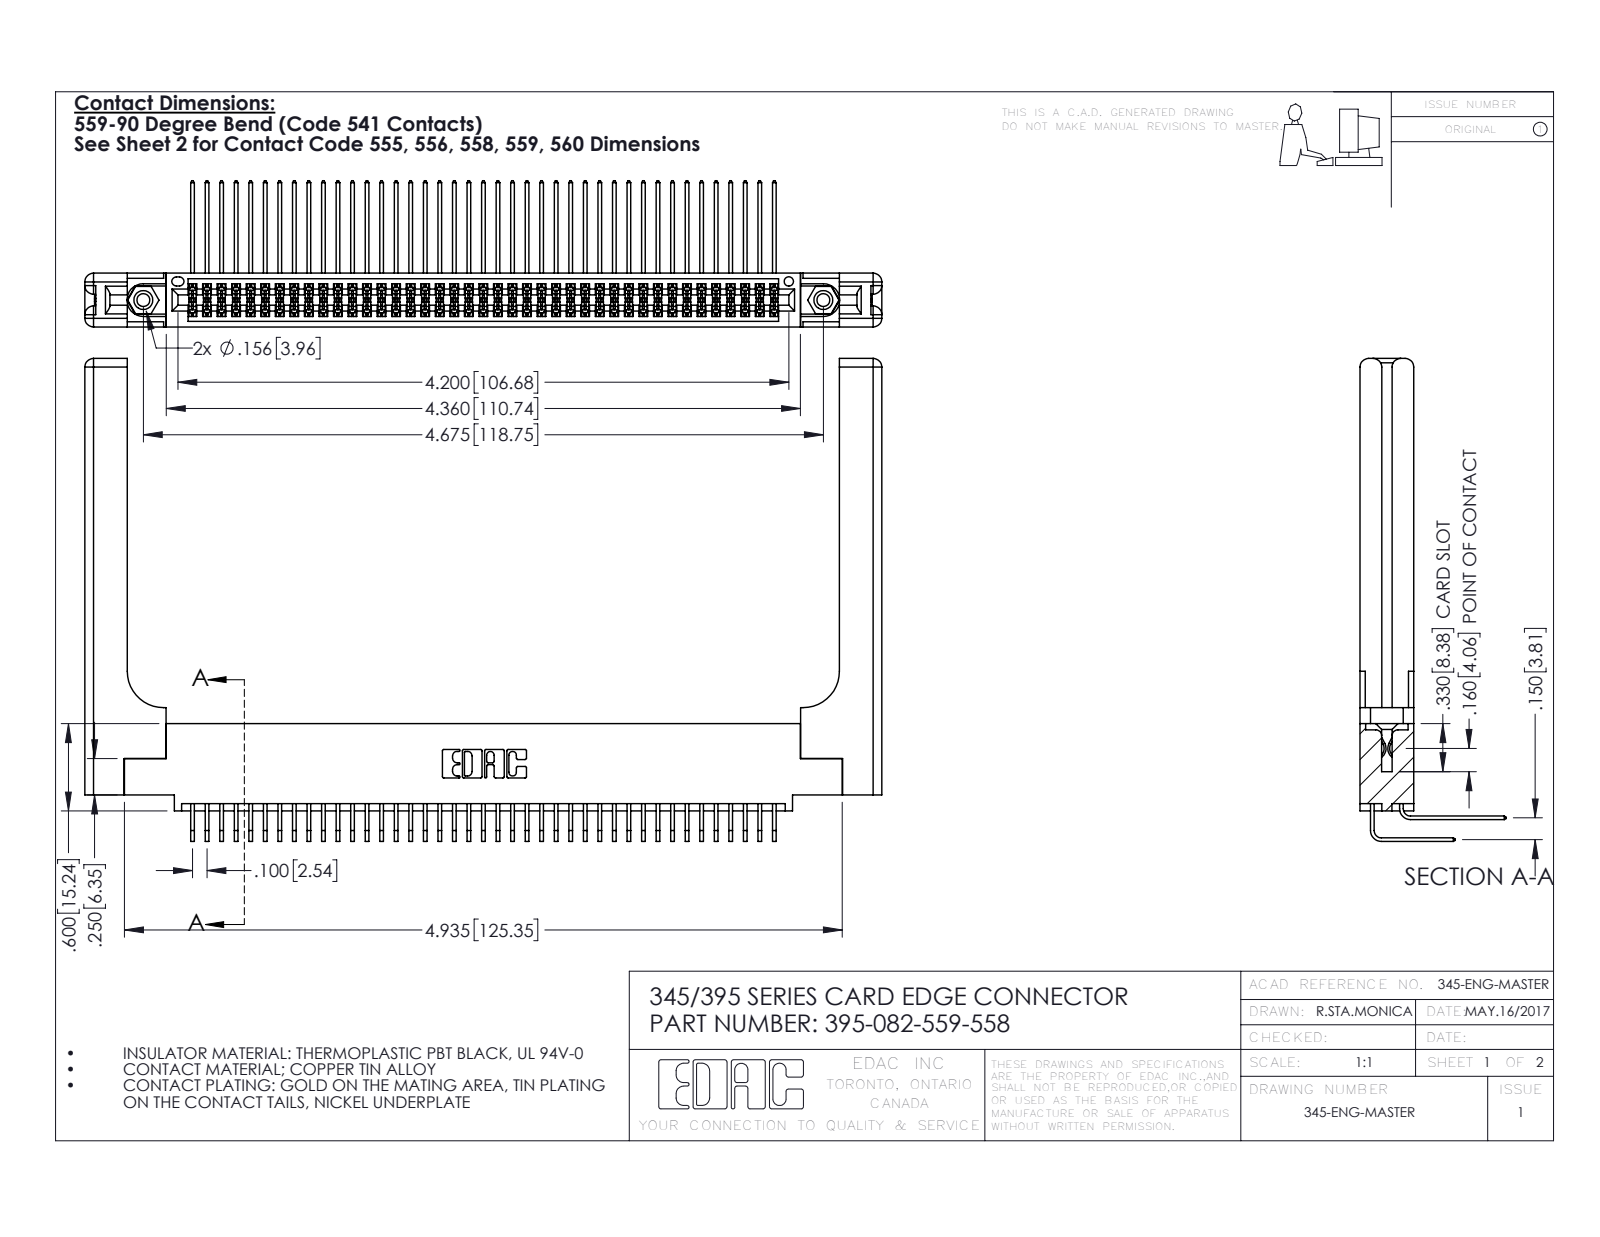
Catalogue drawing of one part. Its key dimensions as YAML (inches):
part_name: "345-250-001_345-250-001-102; 345 Part_0.110 Offset - 0.156 Dia-TH; 395-082-559-558; 345-292-001_558 559 Tail - 1 (+2 more)"
step_written_by: "SolidWorks 2016 (CONFIG_CONTROL_DESIGN)"
units: inches
bodies: {solids: 87, faces: 4650, planar: 3102, cylindrical: 1488, other: 60}
overall_size: [5.479, 3.319, 1.005]
volume: 1.366
surface_area: 43.27
round_holes:
  - {diameter: 0.089, count: 2}
  - {diameter: 0.125, count: 2}
  - {diameter: 0.156, count: 2}
  - {diameter: 0.064, count: 1}
round_bosses_or_shafts:
  - {diameter: 0.155, count: 2}
partial_cylinders:
  - {radius: 0.006, count: 123}
  - {radius: 0.01, count: 22}
  - {radius: 0.06, count: 16}
  - {radius: 0.007, count: 6}
  - {radius: 0.031, count: 6}
  - {radius: 0.026, count: 3}
  - {radius: 0.014, count: 2}
  - {radius: 0.019, count: 2}
face_to_face_distances: [0.072, 0.37, 0.298, 0.2, 0.098, 0.272, 0.025, 0.225, 0.175, 0.15]
hole_center_spacings: [0.27, 4.439, 4.675]
